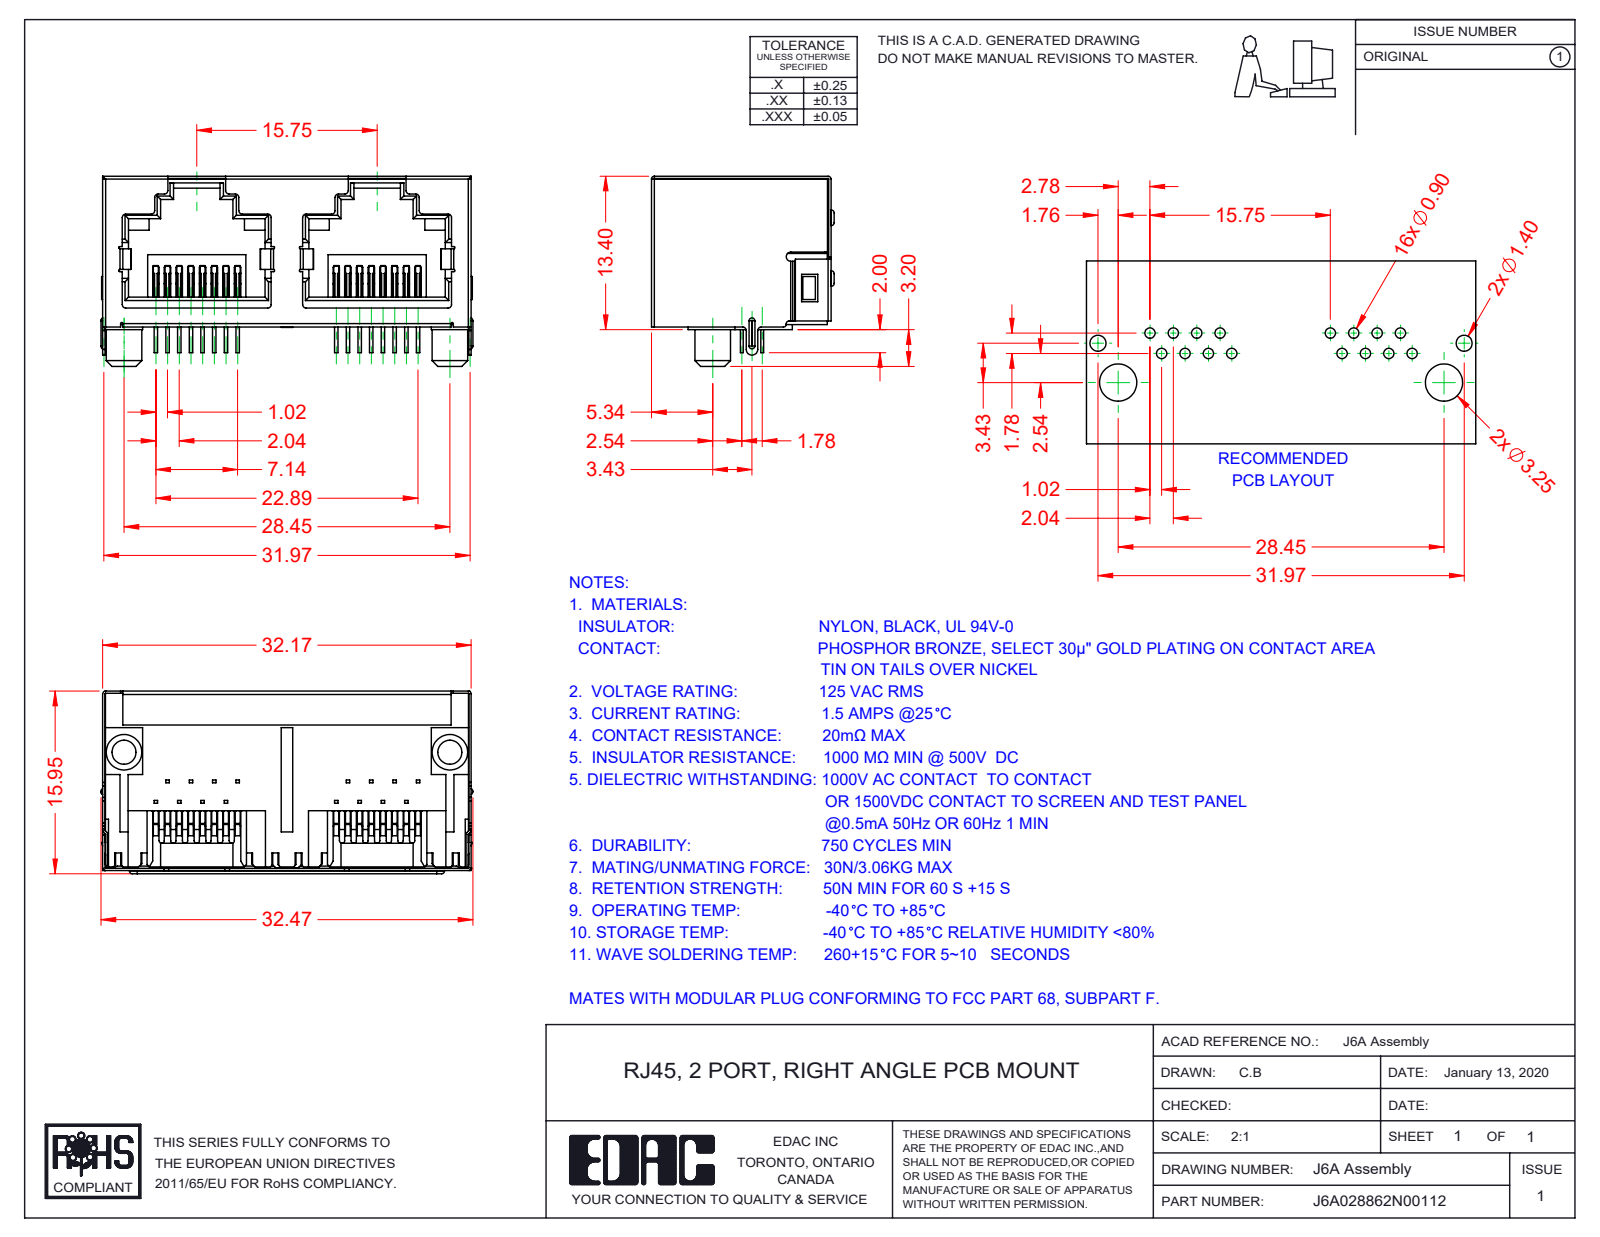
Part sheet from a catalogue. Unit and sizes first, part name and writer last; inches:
Units: inches
Overall size (bounding box): 1.278 × 0.654 × 0.628
Round bosses / shafts (diameter × count): ⌀0.122 ×2
Partial cylindrical surfaces — rounded edges, fillets, slot ends (radius × count): R0.004 ×44, R0.012 ×44, R0.01 ×23, R0.008 ×16, R0.009 ×14, R0.008 ×4, R0.019 ×4, R0.027 ×4
Main face-to-face distances: 0.62, 0.033, 1.259, 0.51, 0.5, 0.502, 0.609, 0.415, 0.079, 0.094
Volume: 0.181 in³ · Surface area: 12.67 in²
Bodies: 18 solids, 1823 faces (1380 planar, 415 cylindrical, 28 other)
Part name (STEP PRODUCT): 6A Shield; 6A Insulator; J6A028862N00112; 6A Contacts
STEP written by: SolidWorks 2016 (CONFIG_CONTROL_DESIGN)
